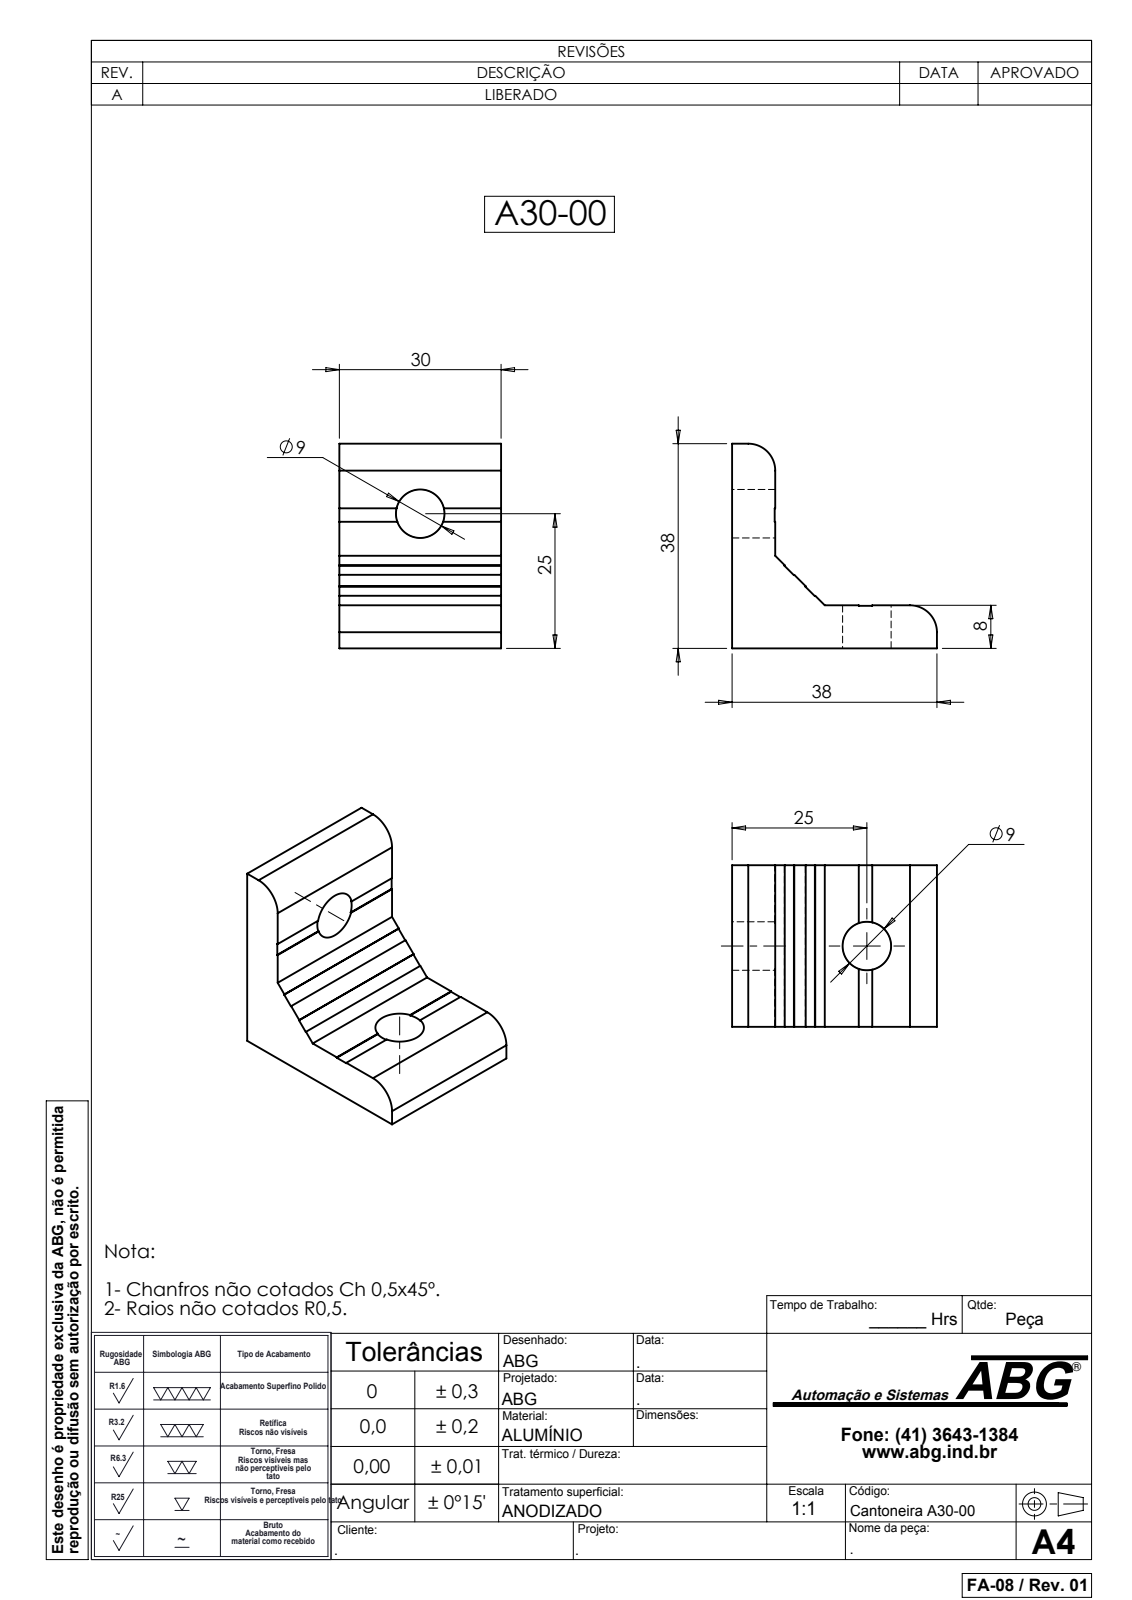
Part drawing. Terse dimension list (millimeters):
name: A30-00
written by: SolidWorks 2007 (CONFIG_CONTROL_DESIGN)
unit: mm
bodies: 1 solid, 37 faces (31 planar, 6 cylindrical, 0 other)
size: 38 × 38 × 30
volume: 16 222 mm³; area: 5 636 mm²
holes: 2× ⌀9
rounds: 2× R5
face distances: 30, 8, 38, 30.1, 7.9, 2.5, 5.5, 14.5, 15.5, 15.6
